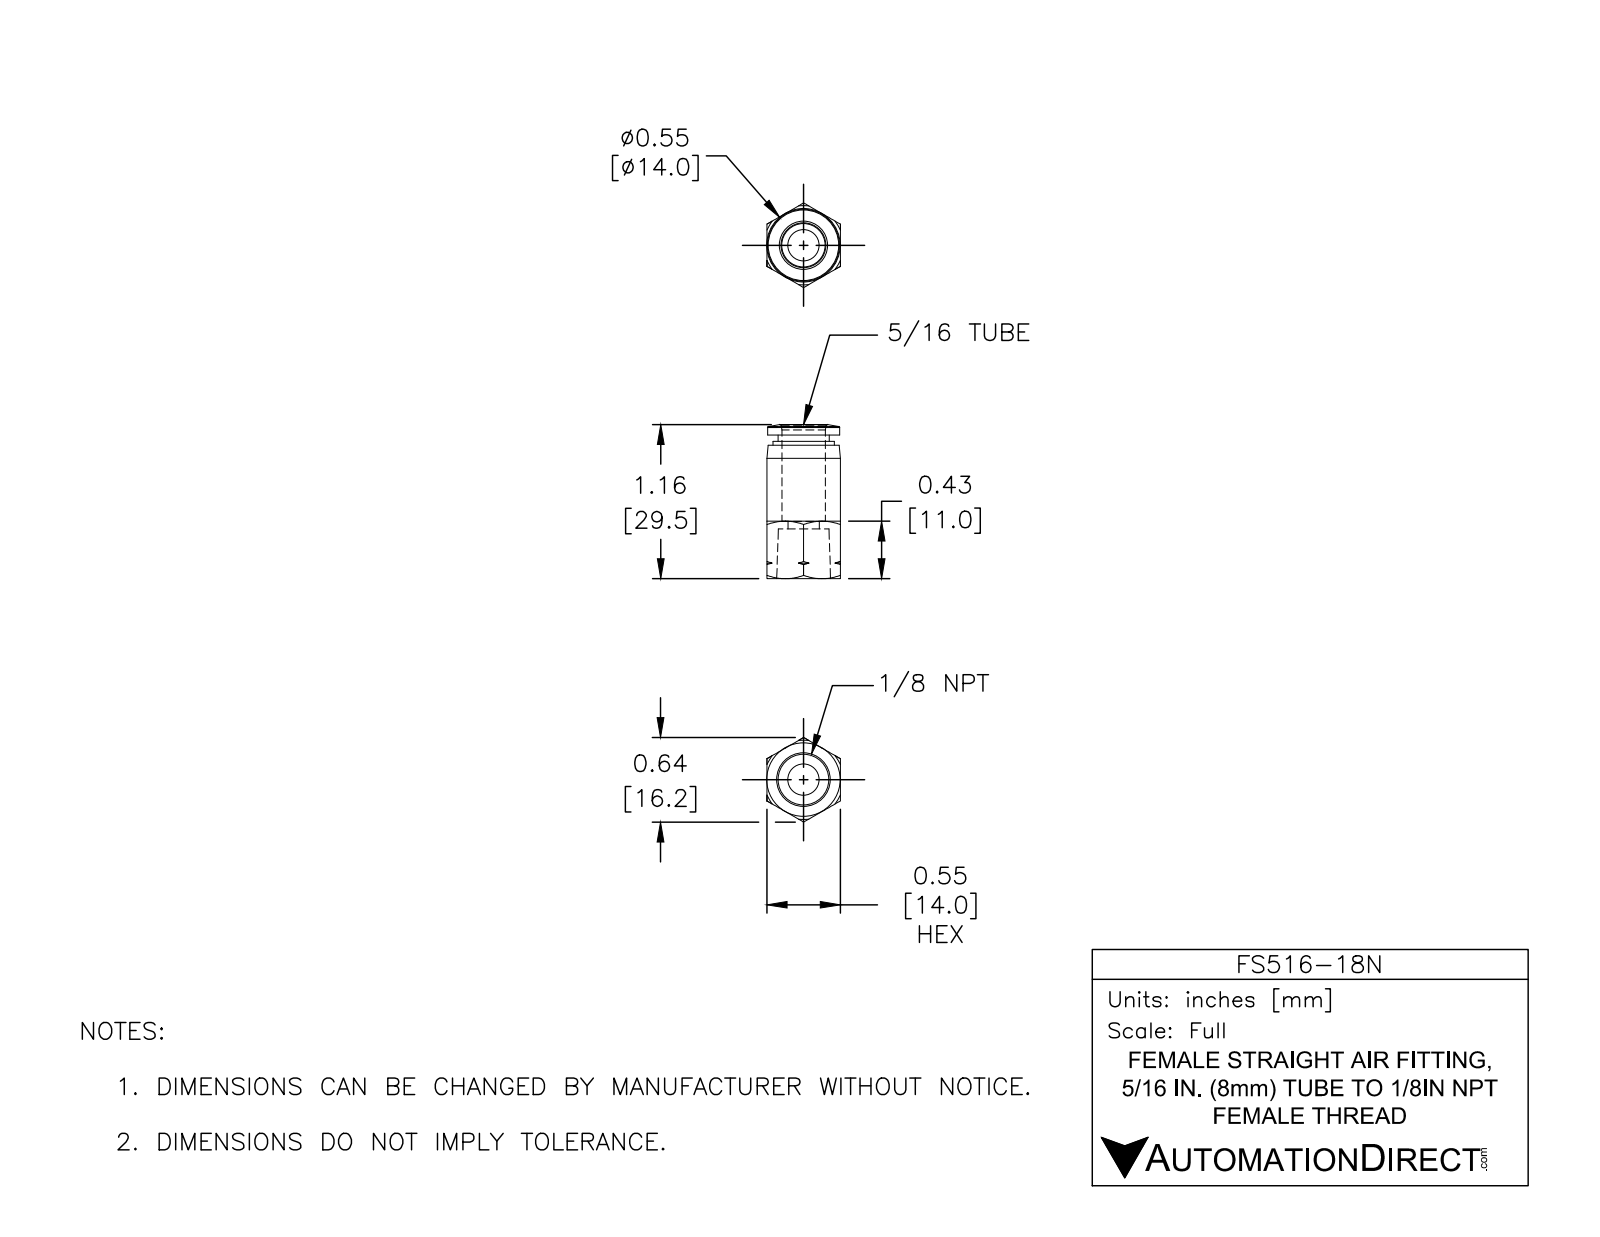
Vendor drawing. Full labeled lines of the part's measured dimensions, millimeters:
Part name (STEP PRODUCT): FS516-18N
STEP written by: SolidWorks 2015 (CONFIG_CONTROL_DESIGN)
Units: millimetres
Bodies: 1 solid, 60 faces (12 planar, 12 cylindrical, 36 other)
Overall size (bounding box): 29.4 × 16.2 × 14
Volume: 2 740 mm³ · Surface area: 2 505 mm²
Round holes (diameter × count): ⌀6 ×1, ⌀8.3 ×1
Round bosses / shafts (diameter × count): ⌀14 ×1, ⌀13.8 ×1, ⌀11.7 ×1, ⌀9.8 ×1
Main face-to-face distances: 14, 27.5, 9.5, 18, 25.5, 16, 2, 26.2, 16.7, 0.8
